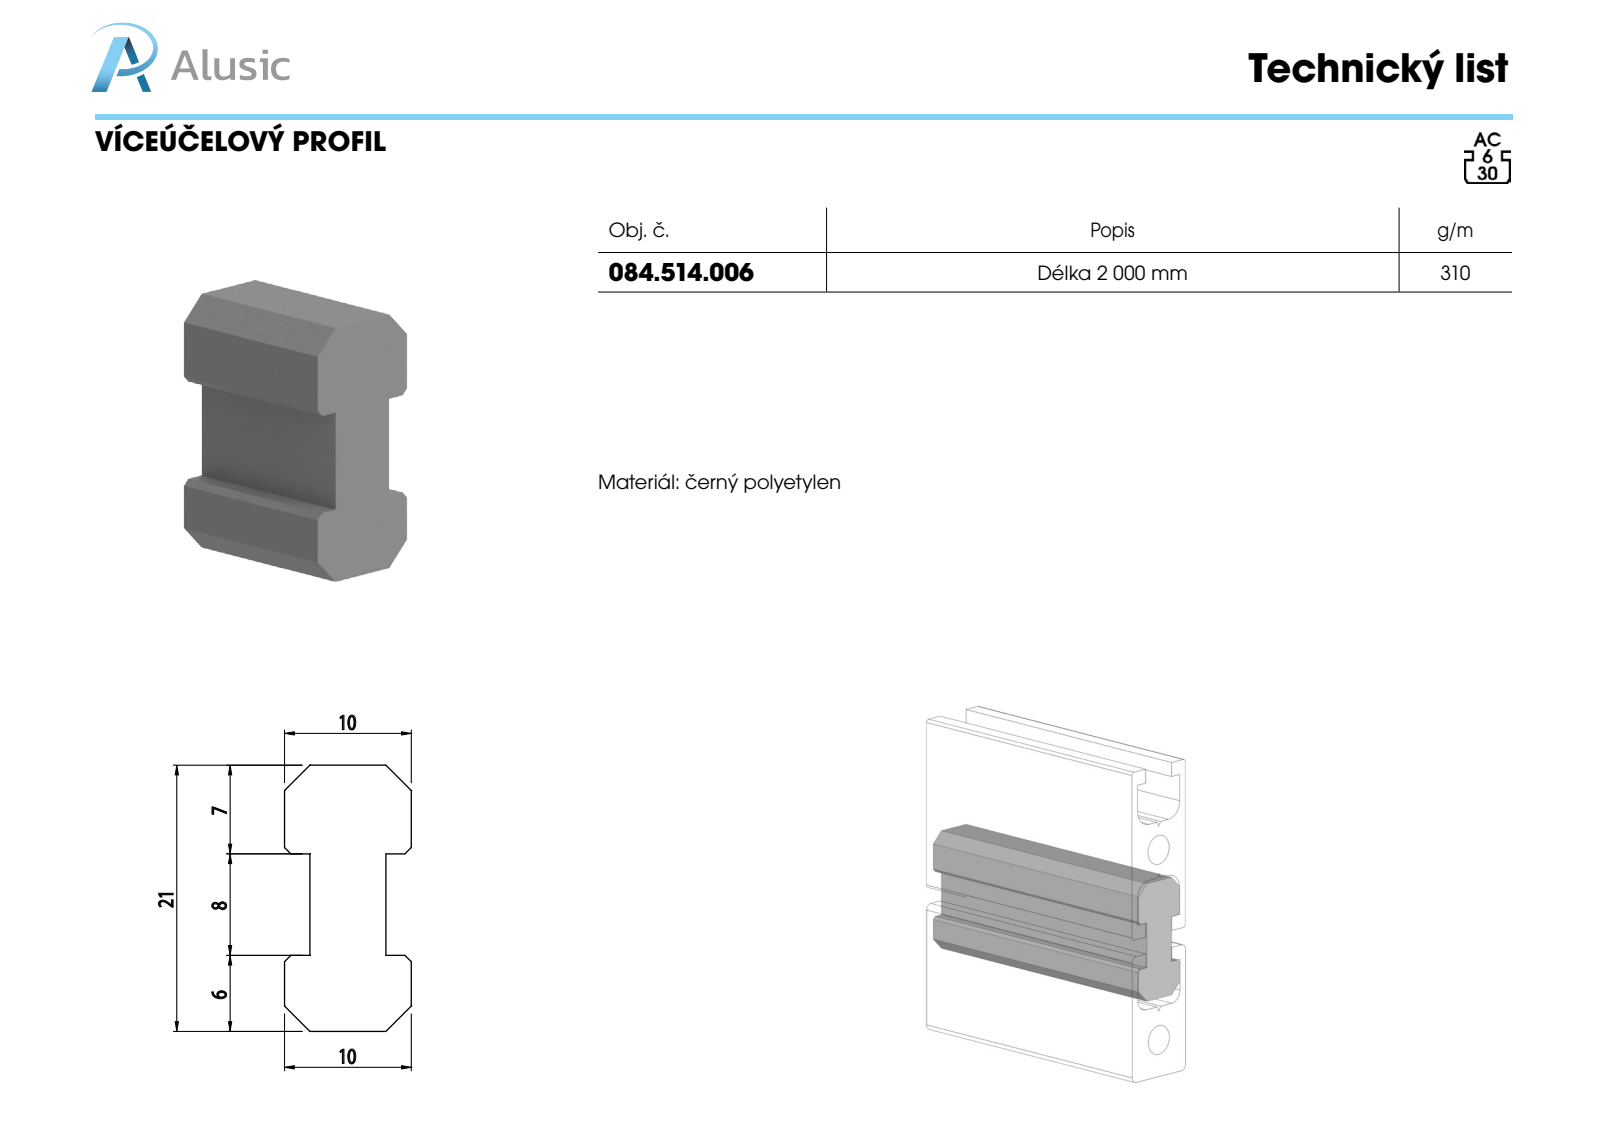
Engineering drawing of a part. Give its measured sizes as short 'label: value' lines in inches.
name: 084.514.006
written by: SolidWorks 2011 (CONFIG_CONTROL_DESIGN)
unit: in
bodies: 1 solid, 22 faces (22 planar, 0 cylindrical, 0 other)
size: 3.937 × 0.827 × 0.394
volume: 1.035 in³; area: 10.47 in²
face distances: 0.079, 0.315, 0.236, 0.394, 0.827, 0.752, 0.552, 0.315, 0.591, 0.276
